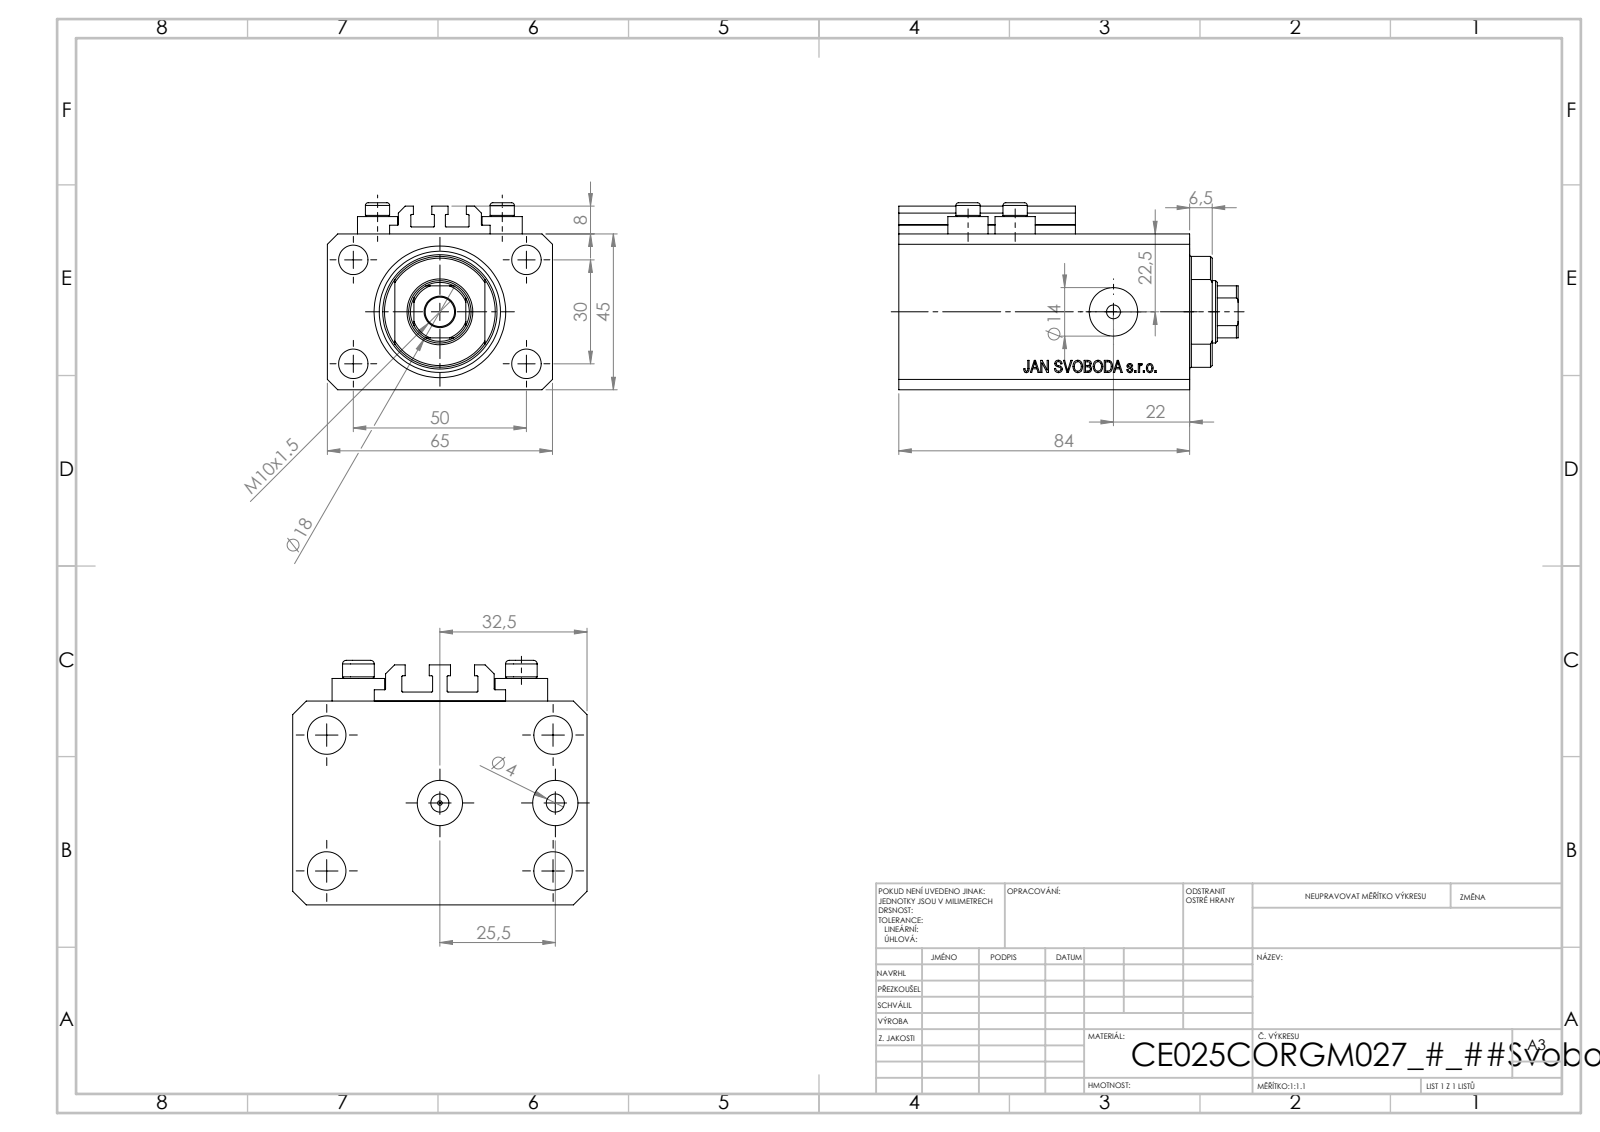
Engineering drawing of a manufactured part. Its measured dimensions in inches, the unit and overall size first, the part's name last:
Units: inches
Overall size (bounding box): 3.858 × 2.559 × 2.126
Round holes (diameter × count): ⌀0.157 ×8, ⌀0.335 ×5, ⌀0.394 ×2, ⌀0.551 ×2, ⌀0.049 ×1, ⌀0.709 ×1, ⌀0.984 ×1, ⌀1.496 ×1
Round bosses / shafts (diameter × count): ⌀0.457 ×4, ⌀0.276 ×4
Partial cylindrical surfaces — rounded edges, fillets, slot ends (radius × count): R0.008 ×10, R0.335 ×1, R0.63 ×1
Main face-to-face distances: 1.772, 2.559, 0.551, 3.307, 2.756, 1.85, 0.272, 2.484, 3.035, 0.118
Hole centre spacings: 1.148, 0.535, 0.591, 1.181, 1.417, 1.515, 1.969, 2.074
Volume: 14 in³ · Surface area: 95.43 in²
Bodies: 8 solids, 1042 faces (504 planar, 92 cylindrical, 446 other)
Part name (STEP PRODUCT): V250CE_C_Body; V250CE_C_VCP; V250CE_VC_C; ALLEN BOLT V250CE
STEP written by: SolidWorks 2019 (CONFIG_CONTROL_DESIGN)
